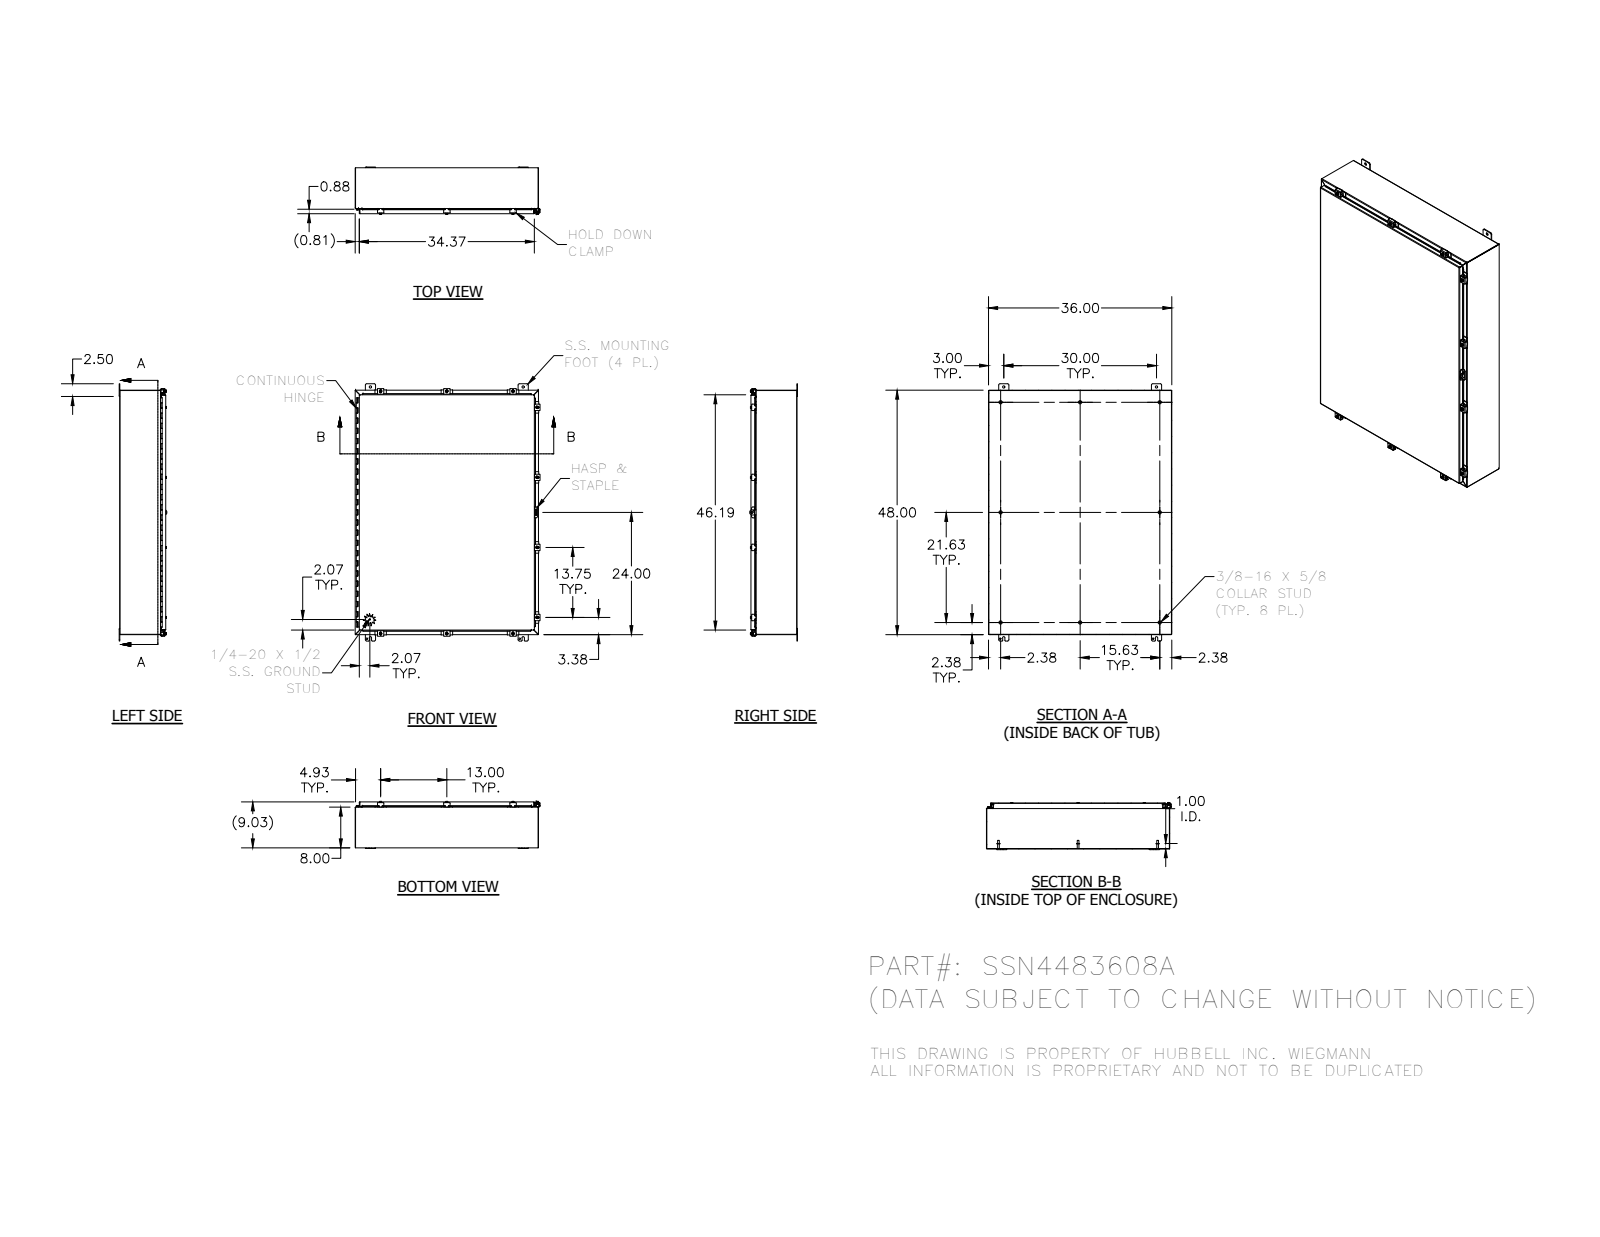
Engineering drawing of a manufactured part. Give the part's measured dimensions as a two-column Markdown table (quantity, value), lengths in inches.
| quantity | value |
| --- | --- |
| part name | HFW308001; 46x34; 3298; HFW30825-4 (+8 more) |
| STEP written by | SolidWorks 2014 (AUTOMOTIVE_DESIGN) |
| units | inches |
| bodies | 73 solids, 2680 faces (1093 planar, 1174 cylindrical, 413 other) |
| overall size | 50.5 × 36.311 × 9.355 |
| volume | 413.4 in³ |
| surface area | 10 950 in² |
| round holes (diameter × count) | 0.211 × 10, 0.281 × 10, 0.3 × 10, 0.313 × 4, 0.438 × 4, 0.125 × 1, 0.156 × 1, 0.5 × 1 |
| round bosses / shafts (diameter × count) | 0.25 × 12, 0.52 × 10, 0.5 × 10, 0.35 × 10, 0.625 × 8, 0.33 × 8, 0.337 × 1, 0.12 × 1 |
| partial cylindrical surfaces (radius × count) | 0.03 × 117, 0.125 × 41, 0.25 × 37, 0.031 × 21, 0.105 × 21, 0.141 × 20, 0.062 × 18, 0.1 × 14 |
| main face-to-face distances | 0.074, 8.959, 8.885, 9.033, 35.926, 47.926, 7.926, 1.033, 35.852, 36 |
| hole center spacings | 13.75, 1.593, 13, 18.091, 27.5, 30, 30.973, 48 |
